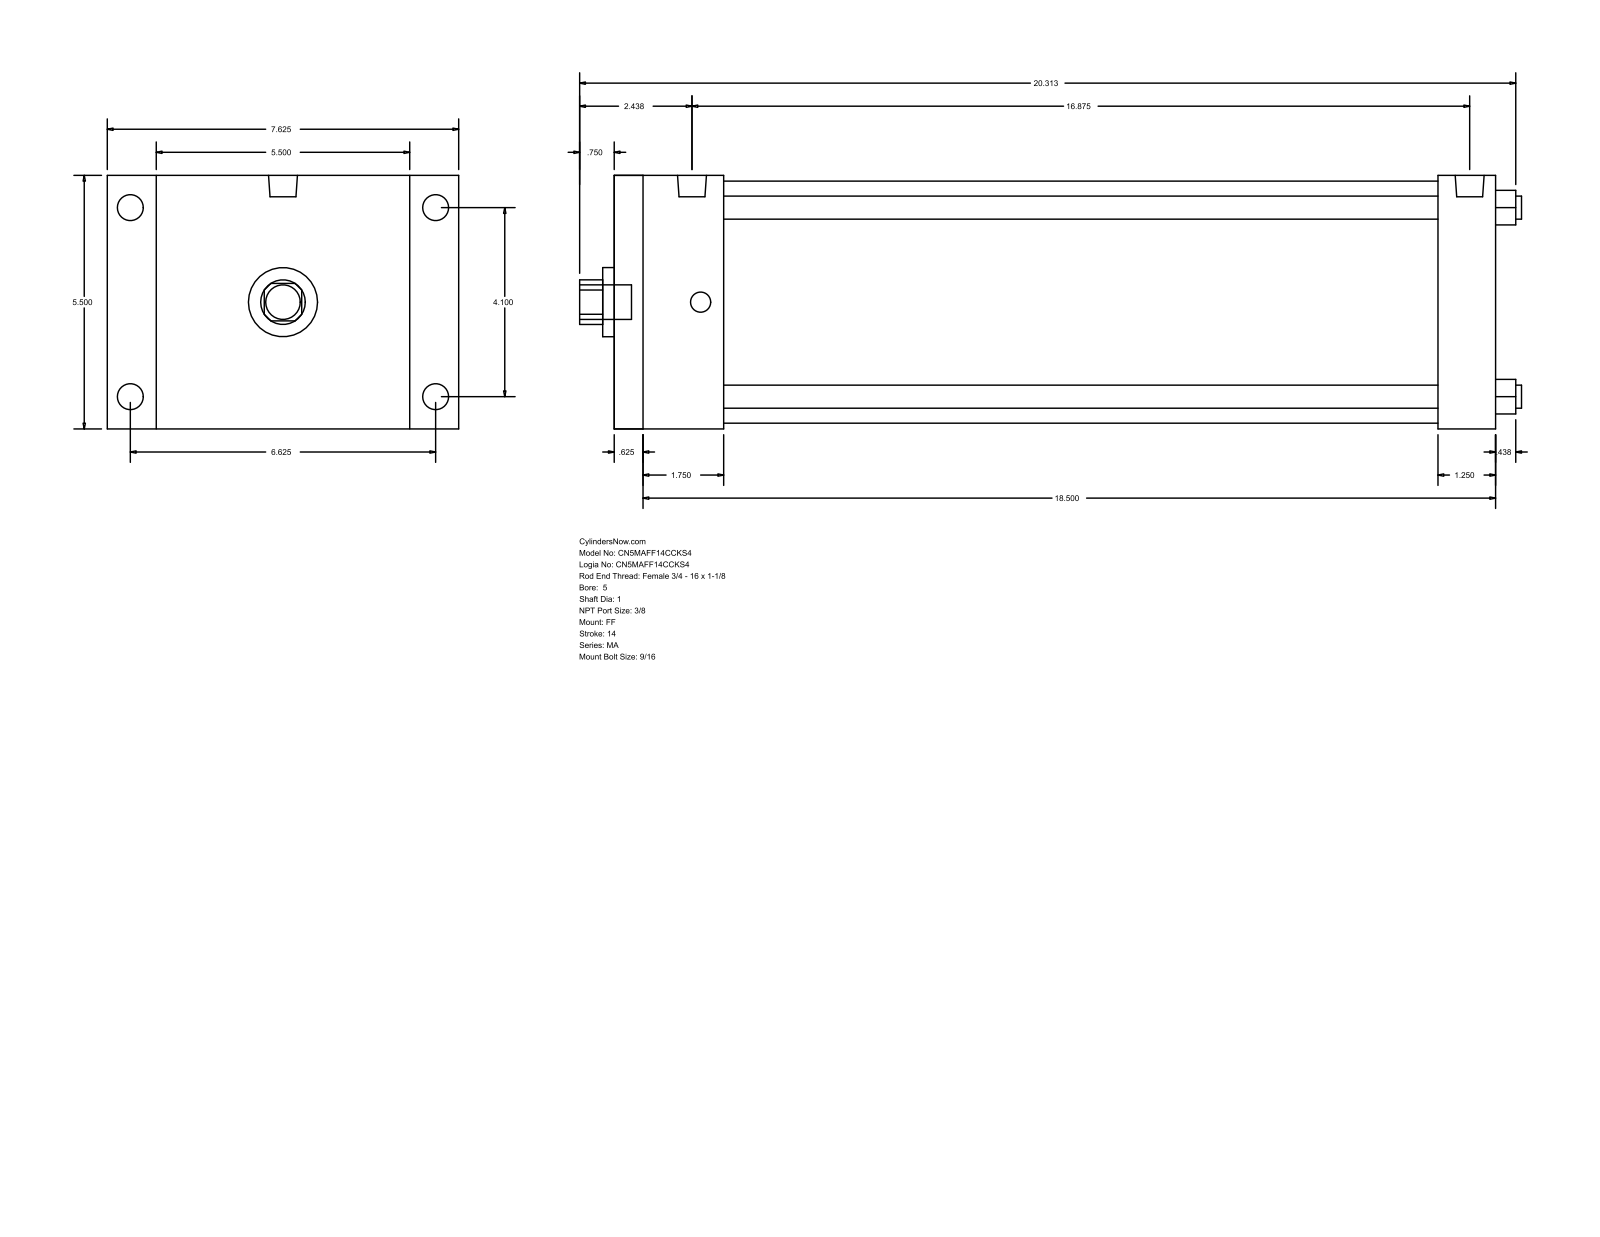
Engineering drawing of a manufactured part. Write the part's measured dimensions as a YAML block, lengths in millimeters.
part_name: "MA_FF__0500_1"
step_written_by: "GSSL Pune (CONFIG_CONTROL_DESIGN)"
units: millimeters
bodies: {solids: 0, faces: 92, planar: 64, cylindrical: 28, other: 0}
overall_size: [519.11, 193.68, 139.7]
round_holes:
  - {diameter: 12.7, count: 4}
  - {diameter: 25.4, count: 1}
  - {diameter: 38.1, count: 1}
  - {diameter: 133.35, count: 1}
round_bosses_or_shafts:
  - {diameter: 14.29, count: 4}
  - {diameter: 11.11, count: 4}
  - {diameter: 15.93, count: 2}
  - {diameter: 19.05, count: 1}
partial_cylinders:
  - {radius: 12.29, count: 1}
face_to_face_distances: [139.7, 485.77, 15.87, 469.9, 454.02, 438.15, 31.75, 60.33, 44.46, 393.69]
hole_center_spacings: [73.64, 104.14, 147.28]
